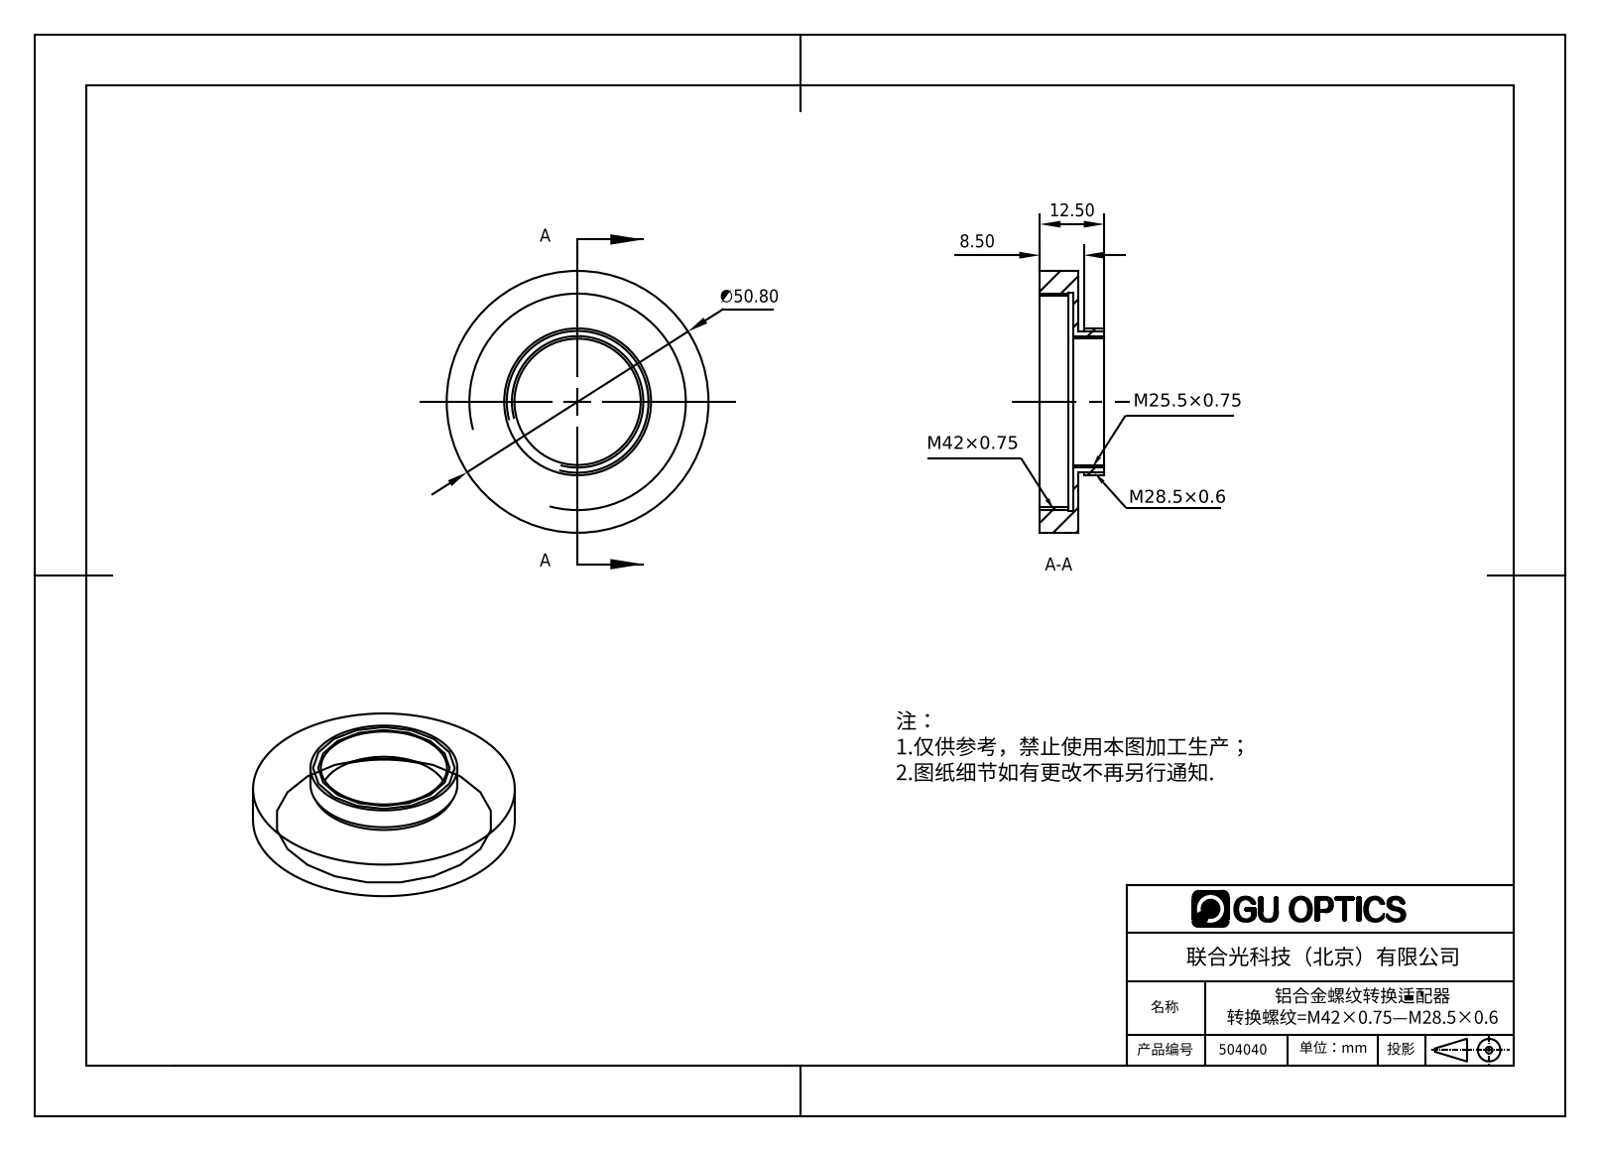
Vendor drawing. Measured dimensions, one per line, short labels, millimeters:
name: 504040
written by: SolidWorks 2016 (AUTOMOTIVE_DESIGN)
unit: mm
bodies: 1 solid, 18 faces (6 planar, 12 cylindrical, 0 other)
size: 50.8 × 50.8 × 12.5
volume: 6 858 mm³; area: 6 300 mm²
holes: 1× ⌀24.5, 1× ⌀41, 1× ⌀42.2
bosses: 1× ⌀50.8, 1× ⌀28.5, 1× ⌀27.5
face distances: 1, 6.5, 7.5, 12.5, 6, 5, 2, 5.5, 7, 8.5
